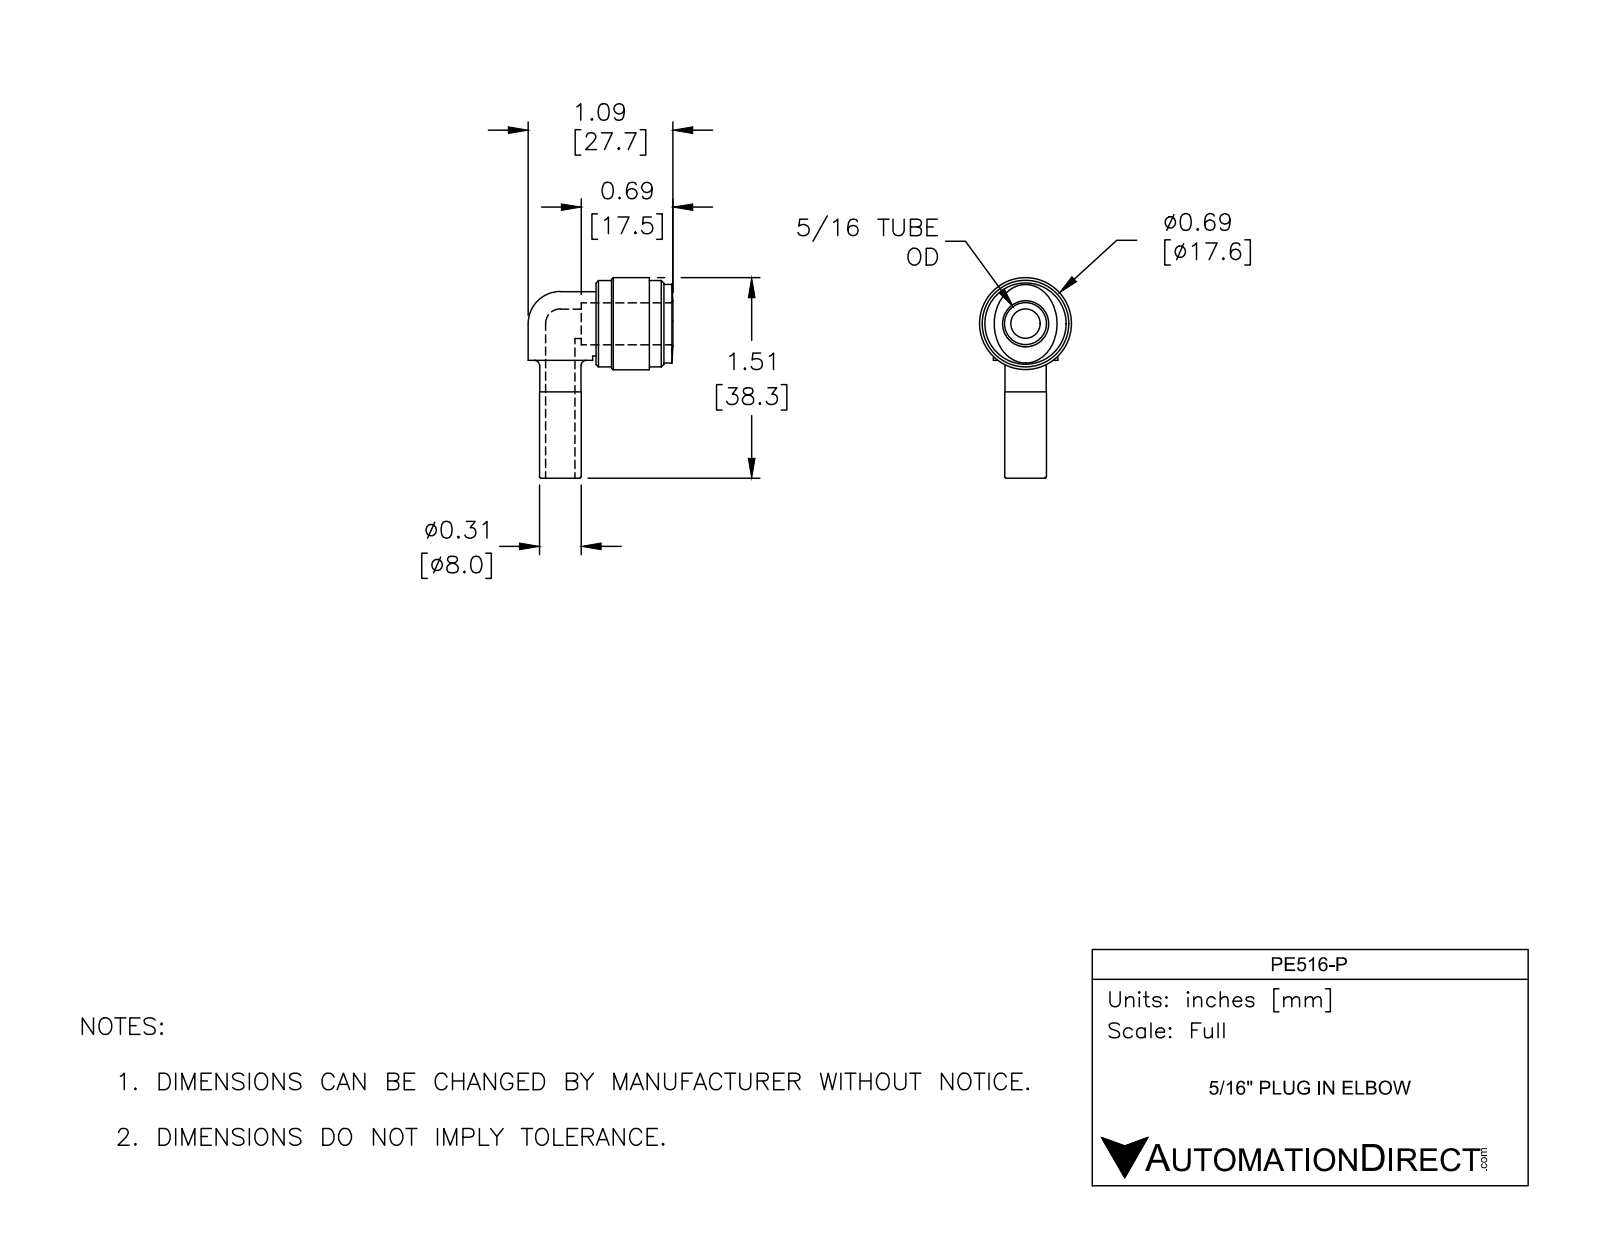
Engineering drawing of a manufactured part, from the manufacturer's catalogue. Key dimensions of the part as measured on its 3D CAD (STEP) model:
Part name (STEP PRODUCT): PE516-P
STEP written by: SolidWorks 2017 (AUTOMOTIVE_DESIGN)
Units: inches
Bodies: 1 solid, 48 faces (8 planar, 20 cylindrical, 20 other)
Overall size (bounding box): 1.508 × 1.089 × 0.693
Volume: 0.257 in³ · Surface area: 5.01 in²
Round holes (diameter × count): ⌀0.22 ×2, ⌀0.315 ×1
Round bosses / shafts (diameter × count): ⌀0.484 ×2, ⌀0.693 ×1, ⌀0.65 ×1, ⌀0.315 ×1, ⌀0.311 ×1
Main face-to-face distances: 0.512, 0.11, 0.402, 0.622, 0.886, 0.228, 0.118, 0.283, 0.394, 0.65
